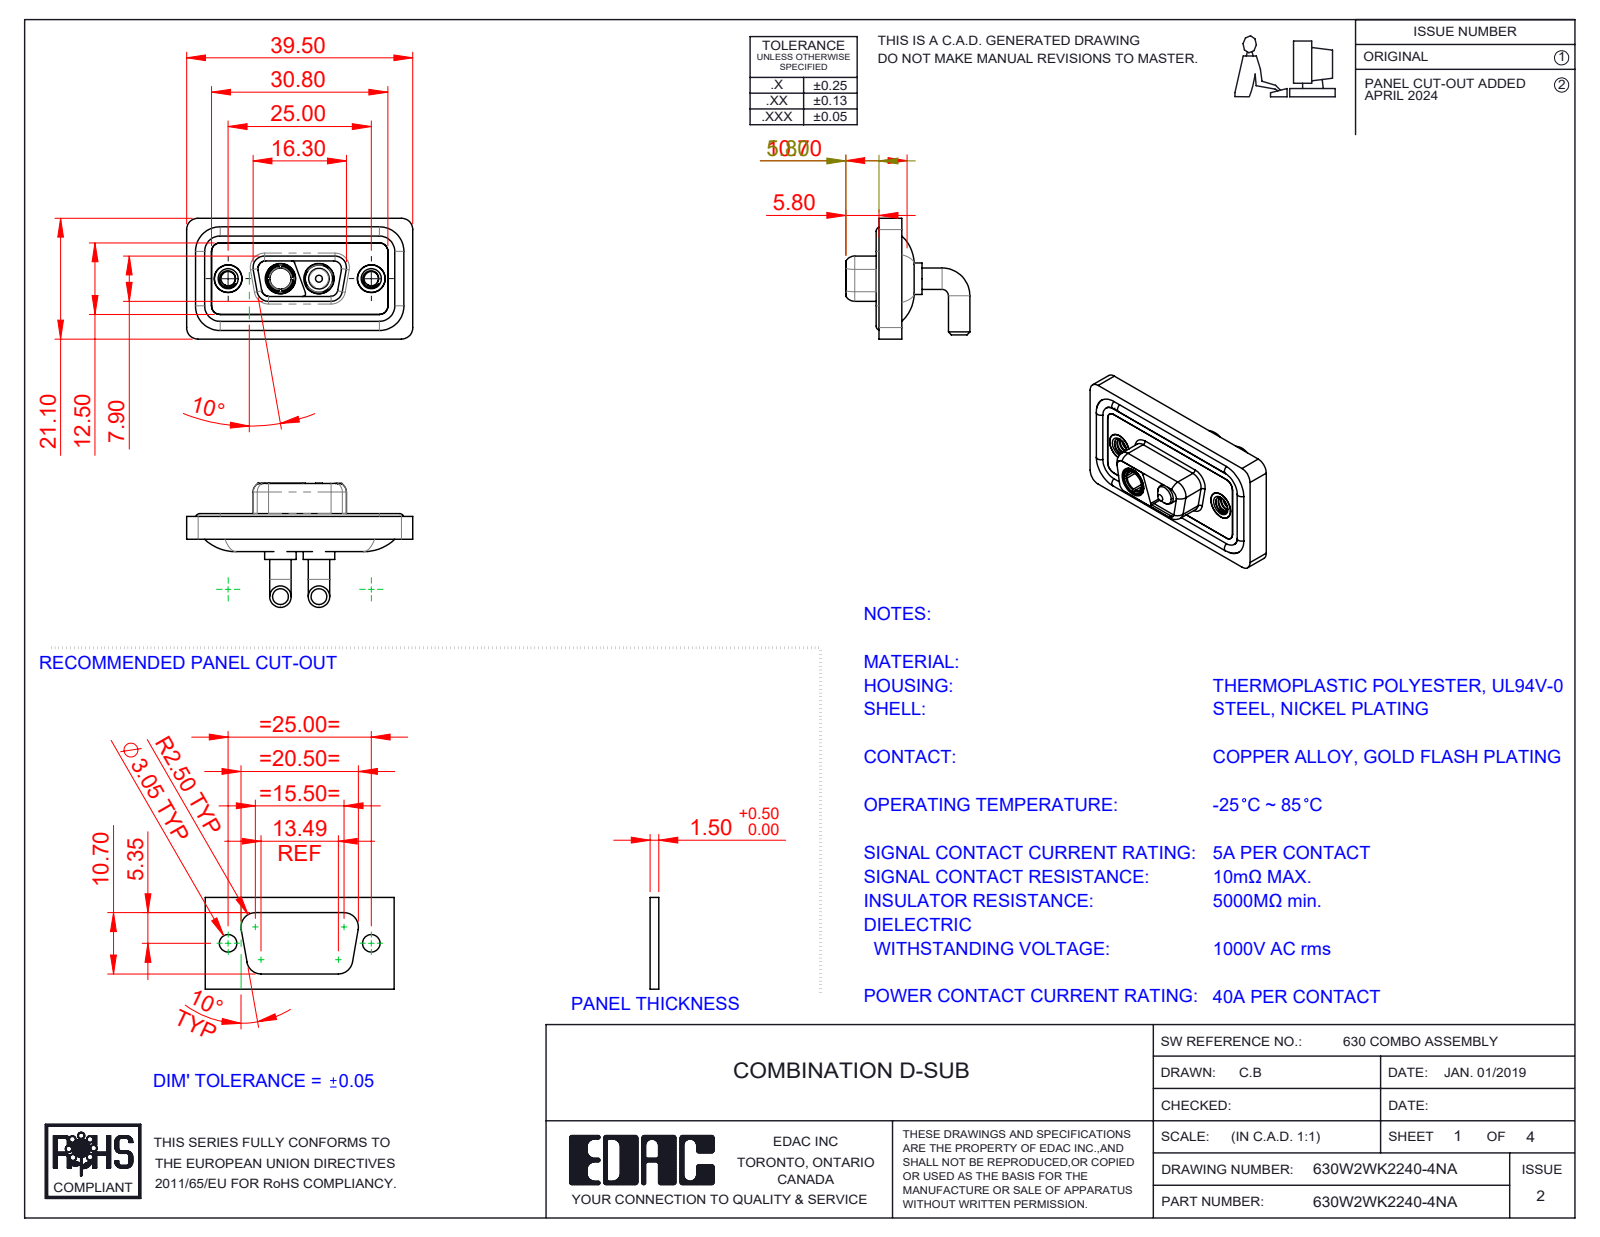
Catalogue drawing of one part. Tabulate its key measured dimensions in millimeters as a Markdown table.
| quantity | value |
| --- | --- |
| part name | Power Pin_40A RA; 630Combo Shell Front_09 Contacts; 630Combo Shell Rear_09 Contacts; 630Combo Waterproof Housing_09 Contacts (+4 more) |
| STEP written by | SolidWorks 2023 (CONFIG_CONTROL_DESIGN) |
| units | millimeters |
| bodies | 11 solids, 502 faces (144 planar, 233 cylindrical, 125 other) |
| overall size | 39.5 × 21.68 × 21.1 |
| volume | 4 845 mm³ |
| surface area | 7 585 mm² |
| round holes (diameter × count) | 4.85 × 4, 2.5 × 2, 4 × 2, 4.05 × 2, 5 × 2, 5.3 × 2, 3.7 × 1 |
| round bosses / shafts (diameter × count) | 3.75 × 4, 1.6 × 4, 5.5 × 2, 5.2 × 2, 4.95 × 2, 4.8 × 2, 4.75 × 2, 4.96 × 1 |
| partial cylindrical surfaces (radius × count) | 1.5 × 18, 2 × 18, 1.35 × 8, 1.6 × 8, 0.5 × 6, 0.25 × 4, 0.6 × 4, 0.65 × 4 |
| main face-to-face distances | 0.4, 1.1, 2.9, 1.8, 2.5, 1.6, 3.1, 2.1, 3.7, 1.5 |
| hole center spacings | 9.14, 15.86, 6.72, 25 |
